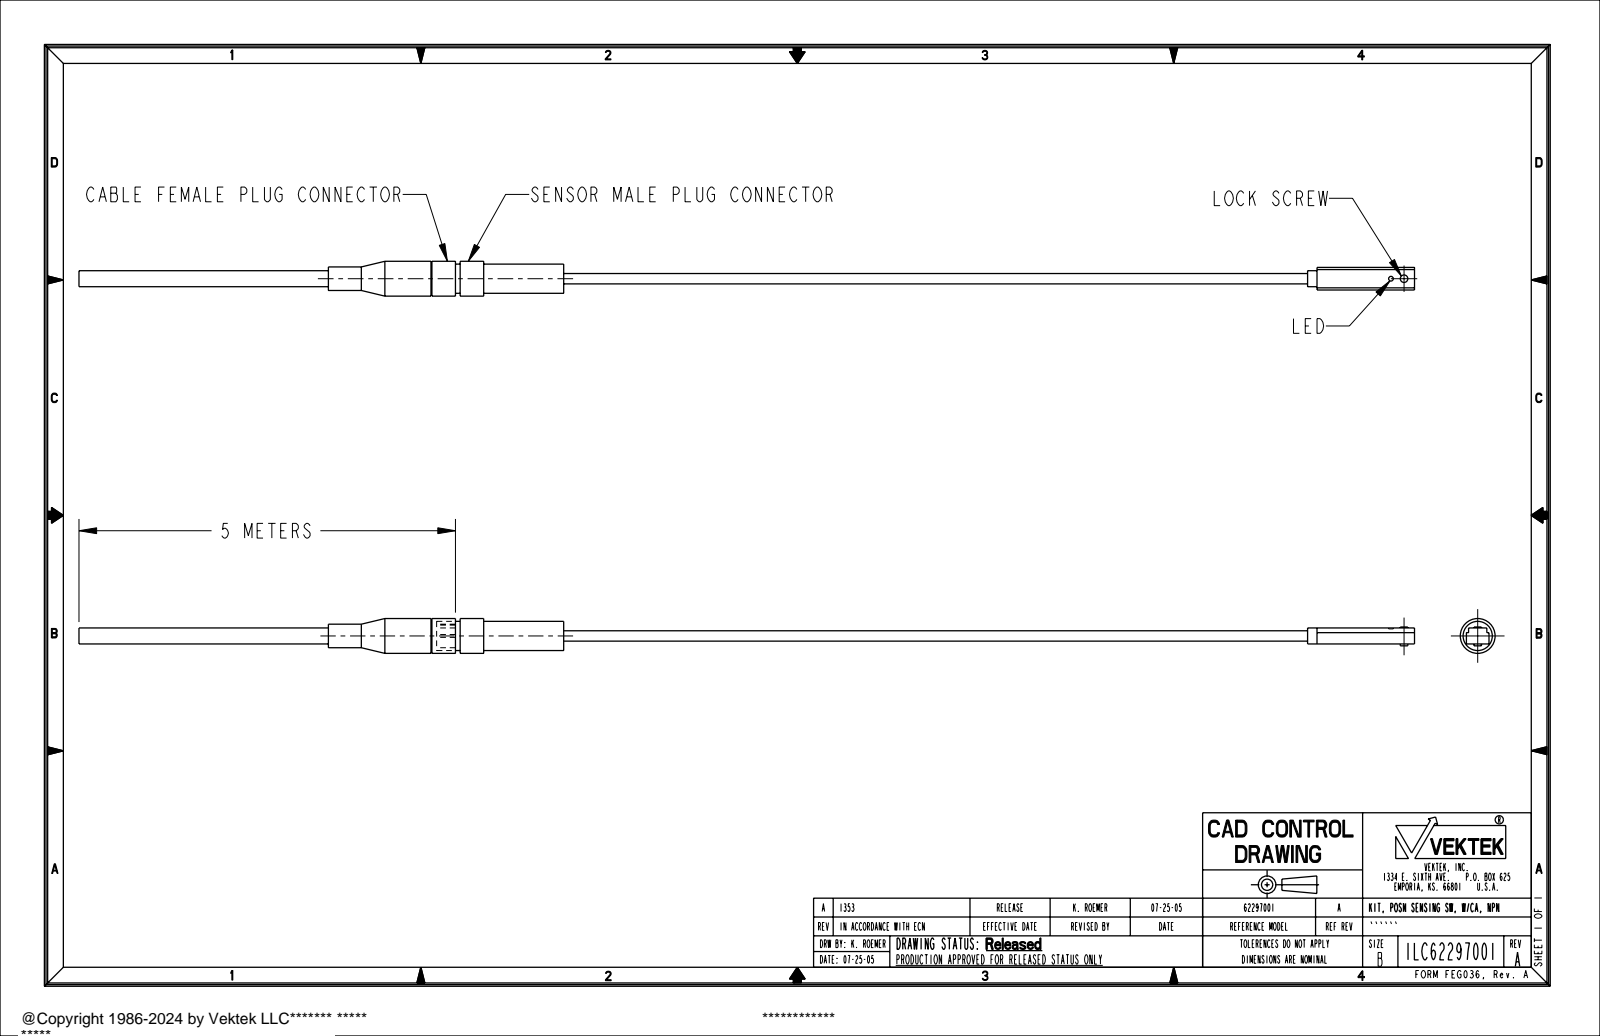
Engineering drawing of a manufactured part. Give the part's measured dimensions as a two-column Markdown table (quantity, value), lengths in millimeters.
| quantity | value |
| --- | --- |
| part name | ILC62297001_29700101; ILC62297001_27642400; ILC62297001_ASM |
| STEP written by | PRO/ENGINEER BY PARAMETRIC TECHNOLOGY CORPORATION, 2004290 (AUTOMOTIVE_DESIGN_CC2) |
| units | millimeters |
| bodies | 2 solids, 79 faces (33 planar, 44 cylindrical, 2 other) |
| overall size | 360.4 × 9.4 × 9.4 |
| volume | 6 370 mm³ |
| surface area | 5 736 mm² |
| round holes (diameter × count) | 0.8 × 3, 1.3 × 1 |
| round bosses / shafts (diameter × count) | 9.4 × 1, 8.9 × 1, 7.9 × 1, 6.4 × 1, 4.3 × 1, 2.8 × 1, 2 × 1 |
| main face-to-face distances | 4.3, 6.1, 0.6, 5.5, 29.2, 1.3, 34.3, 6.4, 5.1, 4.9 |
| hole center spacings | 3.6, 5.1 |
